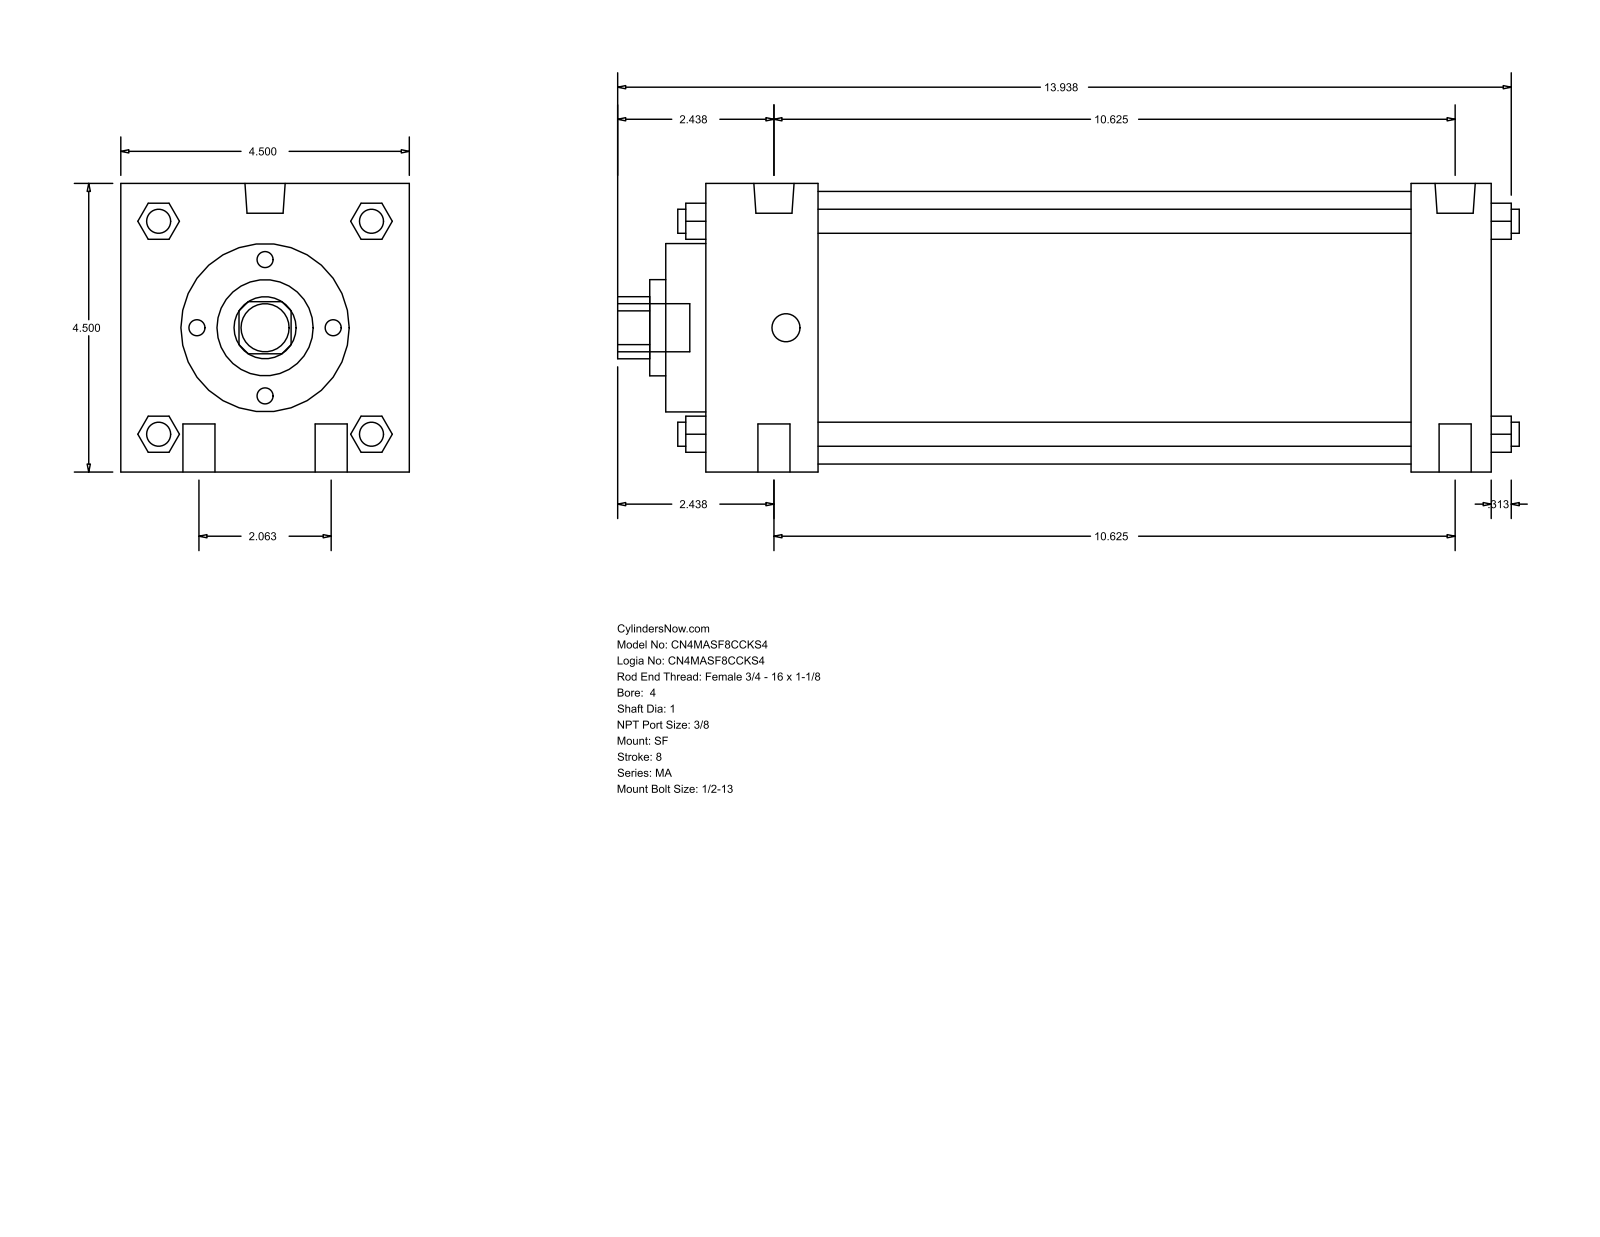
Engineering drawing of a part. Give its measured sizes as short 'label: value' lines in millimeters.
name: MA_SF__0400_1
written by: GSSL Pune (CONFIG_CONTROL_DESIGN)
unit: mm
bodies: 0 solids, 126 faces (95 planar, 31 cylindrical, 0 other)
size: 357.19 × 114.3 × 114.3
holes: 1× ⌀25.4, 1× ⌀38.1, 1× ⌀66.67, 1× ⌀107.95
bosses: 4× ⌀12.7, 4× ⌀9.53, 2× ⌀15.93, 2× ⌀11.11, 1× ⌀19.05
rounds: 1× R12.29
face distances: 114.3, 311.15, 279.4, 31.75, 44.46, 234.94, 266.69, 327.02, 15.87, 60.33
